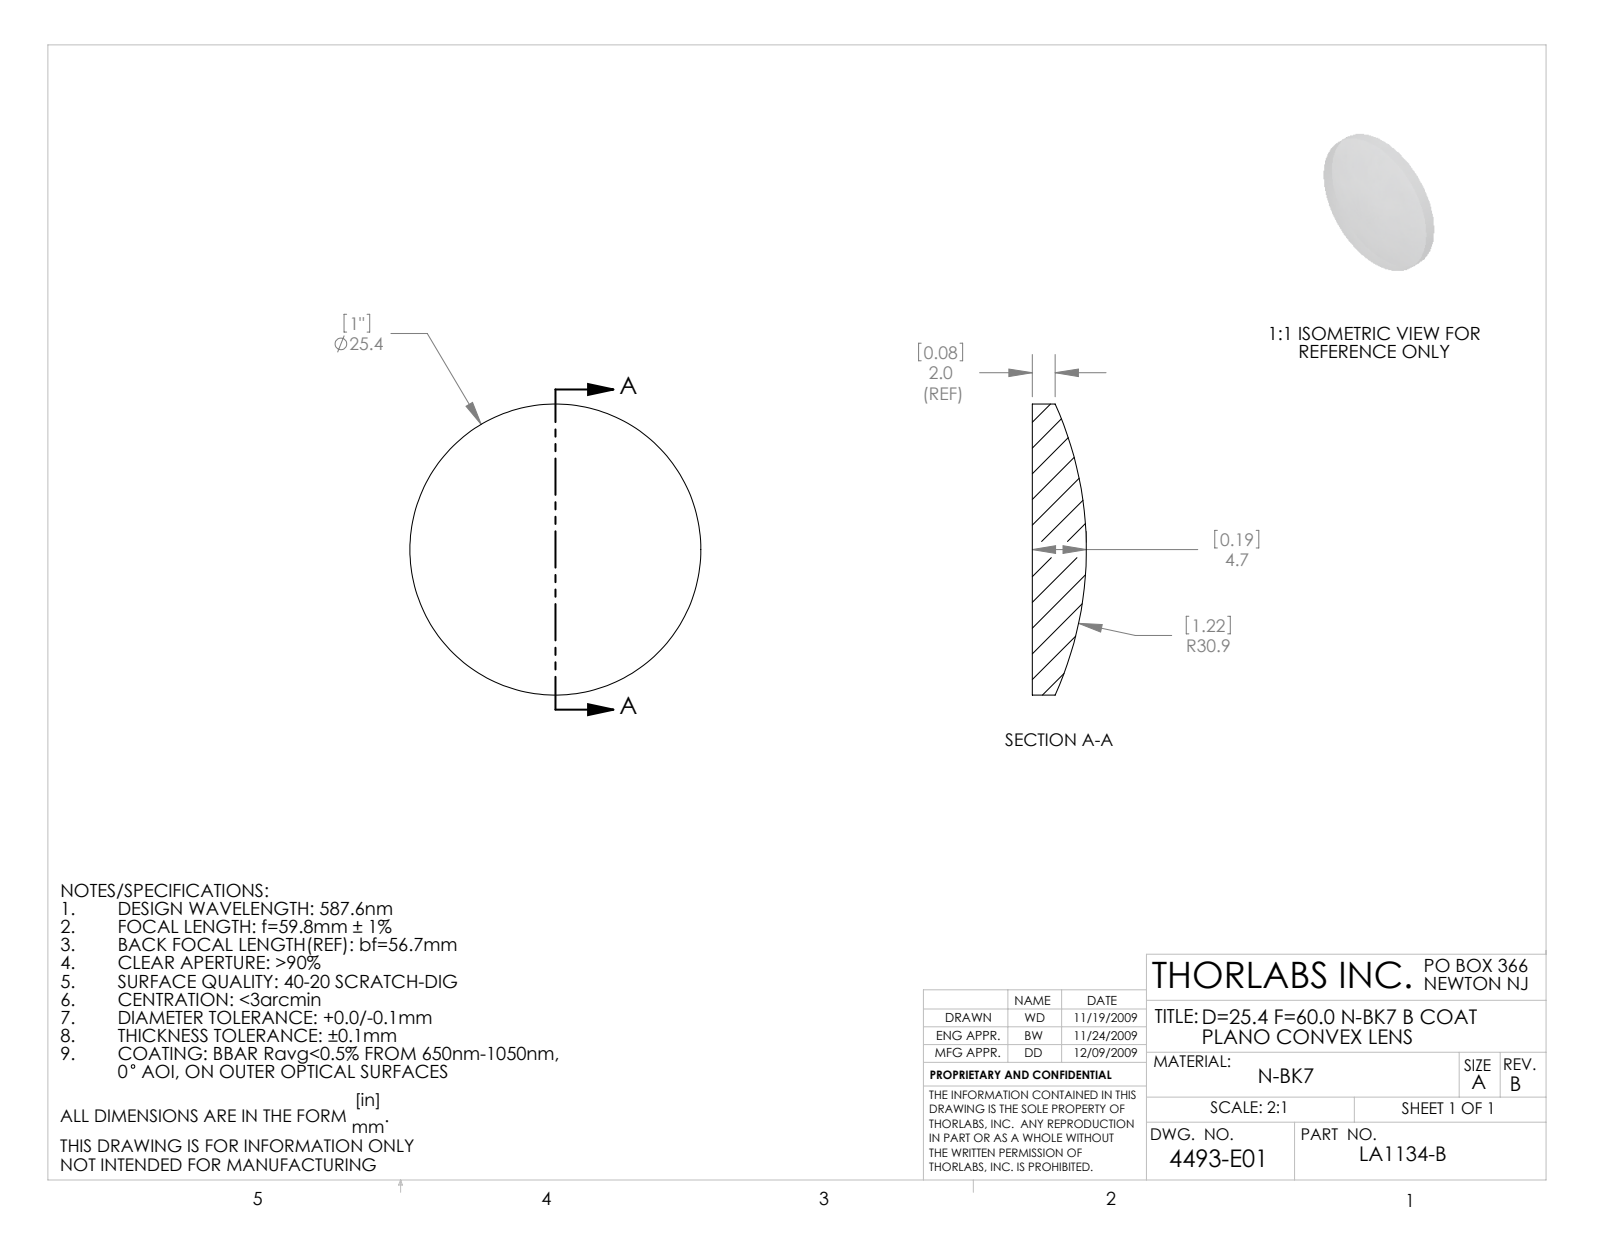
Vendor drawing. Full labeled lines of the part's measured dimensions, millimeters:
Part name (STEP PRODUCT): 4493-E0W
STEP written by: SolidWorks 2009 (AUTOMOTIVE_DESIGN)
Units: millimetres
Bodies: 1 solid, 5 faces (1 planar, 2 cylindrical, 2 other)
Overall size (bounding box): 25.4 × 25.4 × 4.73
Volume: 1 716 mm³ · Surface area: 1 196 mm²
Round bosses / shafts (diameter × count): ⌀25.4 ×1
